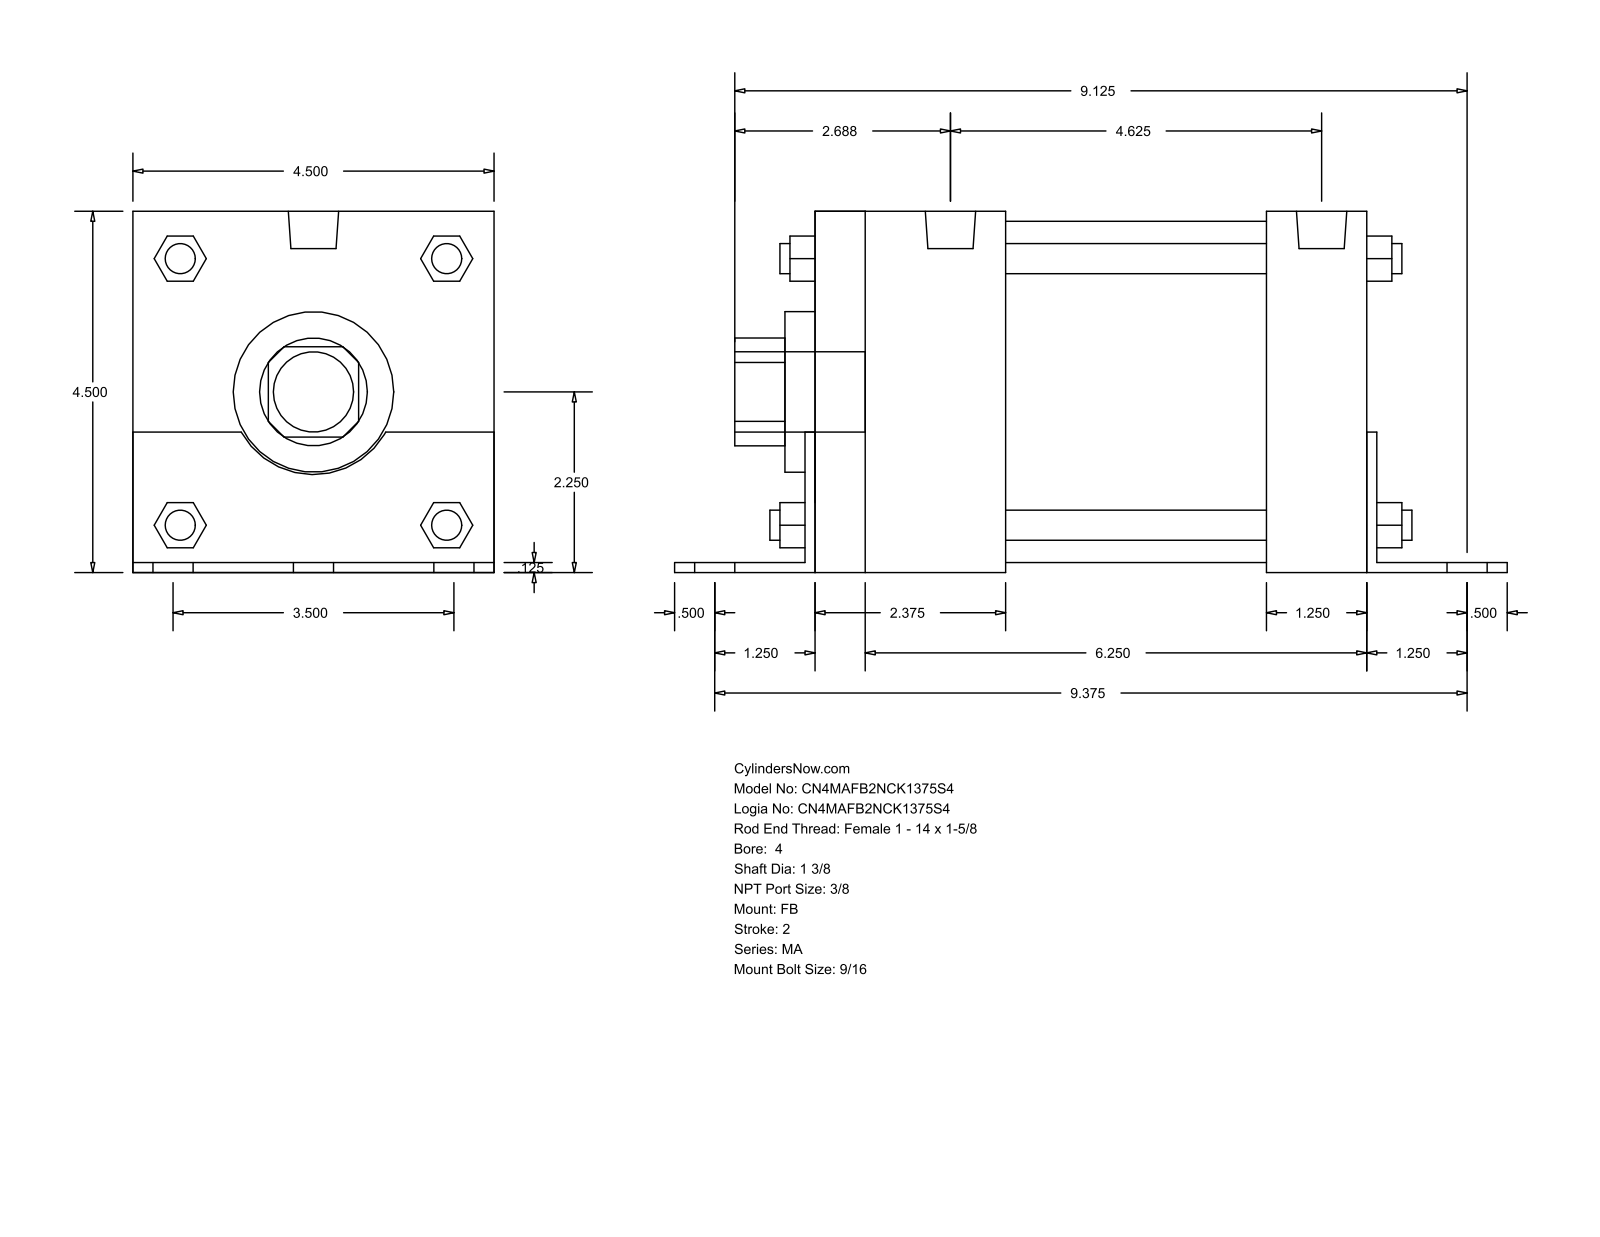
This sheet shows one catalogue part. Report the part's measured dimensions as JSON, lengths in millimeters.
{"part_name": "MA_FB__0400_1.375", "step_written_by": "GSSL Pune (CONFIG_CONTROL_DESIGN)", "units": "millimeters", "bodies": {"solids": 0, "faces": 140, "planar": 105, "cylindrical": 35, "other": 0}, "overall_size": [263.52, 114.35, 114.3], "round_holes": [[34.92, 1], [50.8, 1], [107.95, 1]], "round_bosses_or_shafts": [[14.29, 6], [11.11, 4], [9.53, 4], [15.93, 2], [25.4, 1]], "partial_cylinders_radius": [[17.06, 1], [26.16, 1]], "face_to_face_distances": [114.3, 3.17, 114.35, 3.12, 111.18, 177.8, 174.63, 60.32, 180.97, 31.75]}
